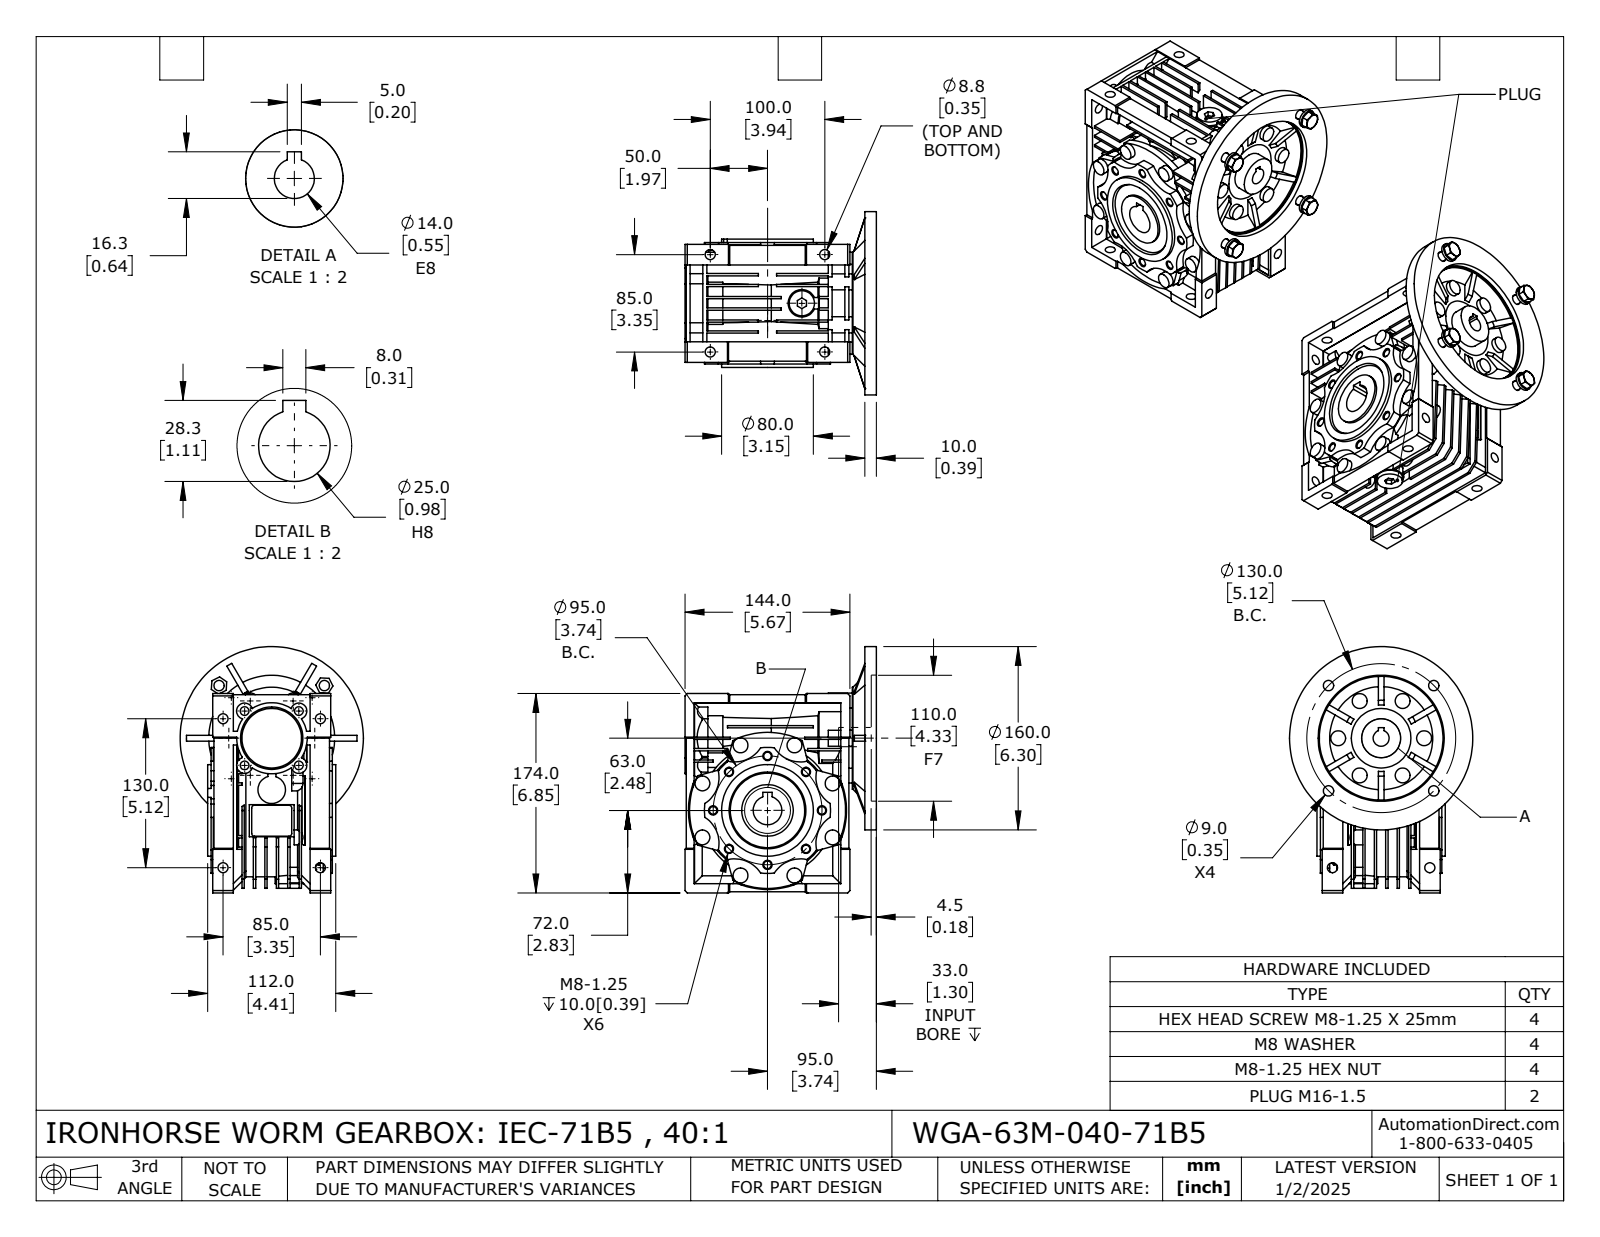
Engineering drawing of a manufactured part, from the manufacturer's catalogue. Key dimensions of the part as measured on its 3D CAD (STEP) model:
Part name (STEP PRODUCT): WGA-63M-040-71B5
STEP written by: SolidWorks 2024 (CONFIG_CONTROL_DESIGN)
Units: millimetres
Bodies: 20 solids, 1516 faces (887 planar, 379 cylindrical, 250 other)
Overall size (bounding box): 215 × 182.98 × 160
Volume: 1 919 000 mm³ · Surface area: 371 344 mm²
Round holes (diameter × count): ⌀6.65 ×8, ⌀8.78 ×8, ⌀6.8 ×4, ⌀7.56 ×4, ⌀8 ×4, ⌀9 ×4, ⌀9.12 ×4, ⌀14.5 ×2, ⌀14 ×1, ⌀15 ×1, ⌀25 ×1, ⌀34 ×1
Round bosses / shafts (diameter × count): ⌀13 ×14, ⌀16 ×4, ⌀24 ×3, ⌀22 ×2, ⌀15.8 ×2, ⌀13.7 ×2, ⌀160 ×1, ⌀110 ×1
Partial cylindrical surfaces — rounded edges, fillets, slot ends (radius × count): R7 ×10, R27 ×8, R2.5 ×4, R8.35 ×1, R29.5 ×1, R30.5 ×1, R42 ×1, R58 ×1
Main face-to-face distances: 10, 8, 20, 2, 30, 12, 7, 18, 40, 1
Hole centre spacings: 36.36, 47.5, 67.18, 73.12, 87.77, 31.49, 33.5, 47.38
